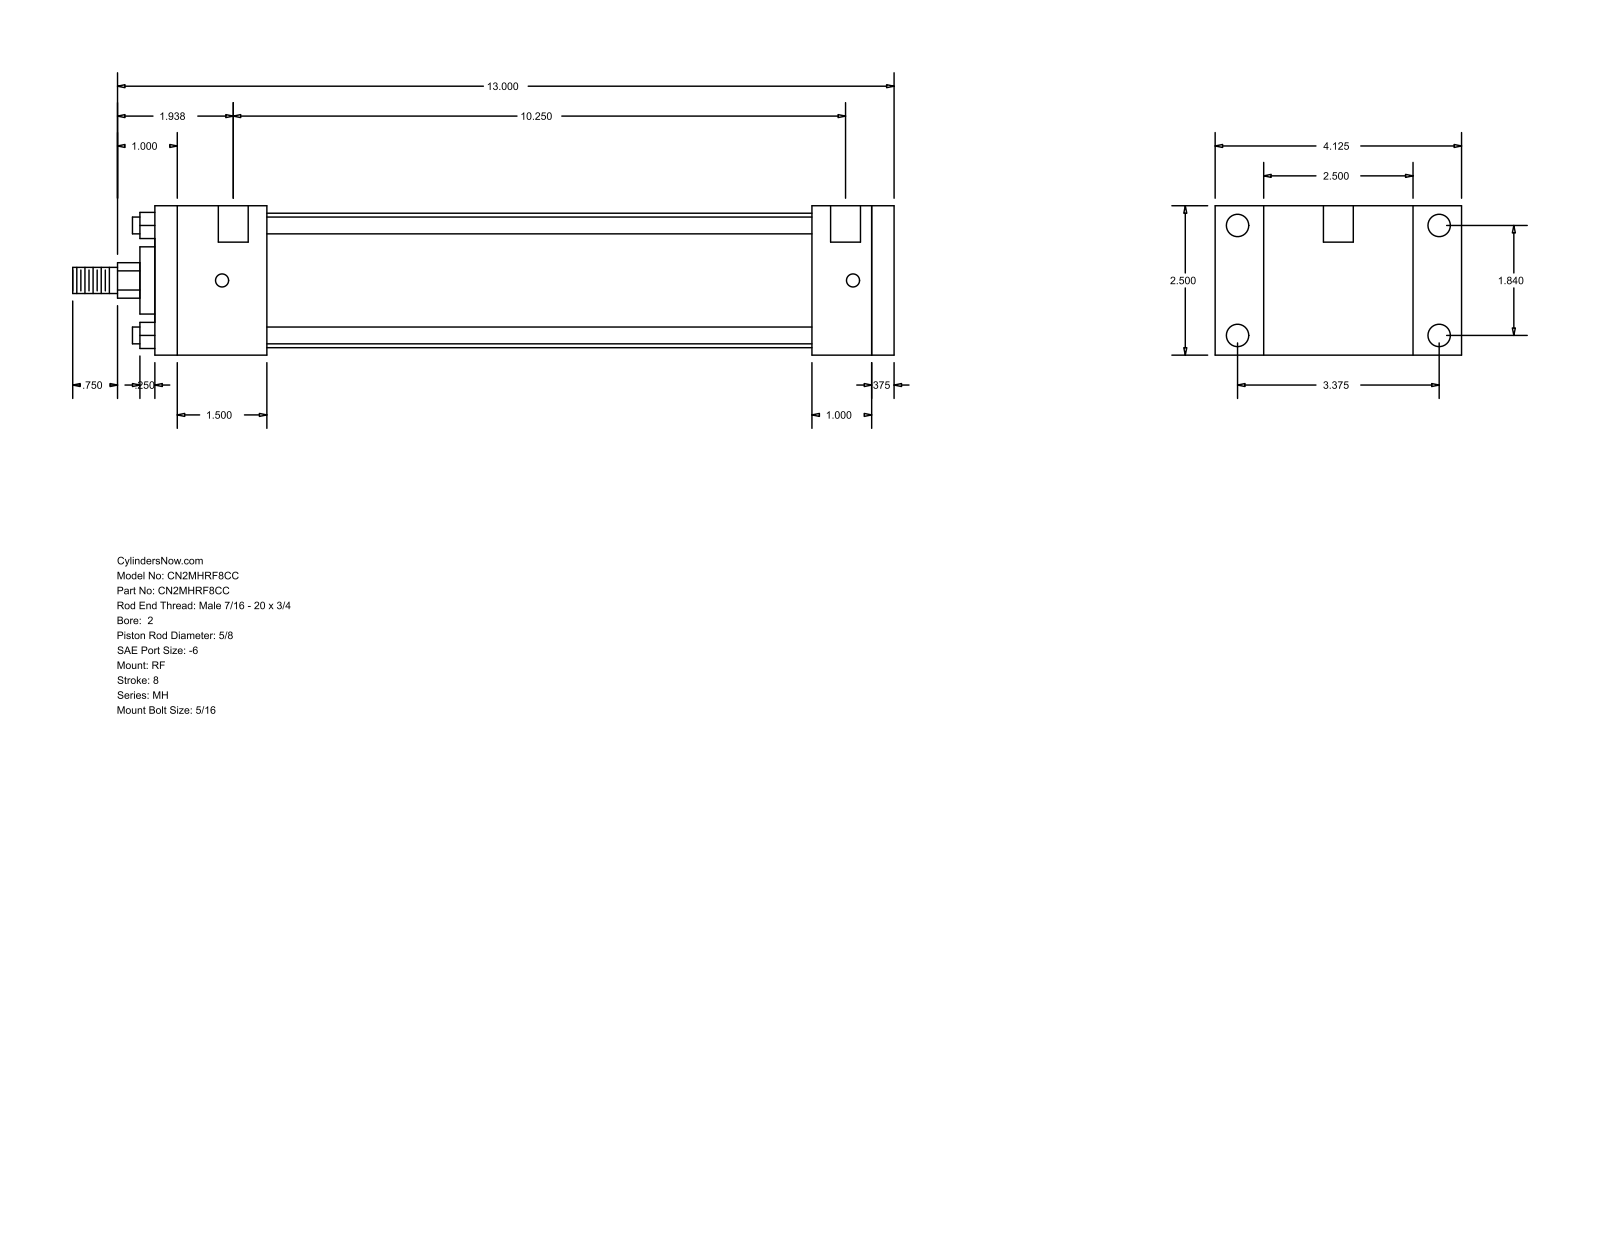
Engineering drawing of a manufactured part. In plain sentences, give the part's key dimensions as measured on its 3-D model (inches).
The part is named "MH_RF__0200_0.625". Its 3-D file was written by "GSSL Pune (CONFIG_CONTROL_DESIGN)". It is 0 solids with 92 faces: 64 planar, 28 cylindrical and 0 other. Overall it measures 13.75 by 4.125 by 2.5 inches. Round holes: 4 of diameter 0.219, 4 of diameter 0.375, 2 of diameter 0.5. Round bosses or shafts: 4 of diameter 0.281, 1 of diameter 2.25, 1 of diameter 1.125, 1 of diameter 0.625, 1 of diameter 0.437. Partial cylindrical surfaces (rounded edges, fillets, slot ends): 1 of radius 0.297. The main face-to-face distances are 2.5, 12.375, 12, 0.375, 1.375, 1.875, 11, 9.125, 10.125, 10.5. The hole center spacings are 1.84, 3.375, 3.844, 10.563, 0.125, 0.187, 10.25, 10.375.
